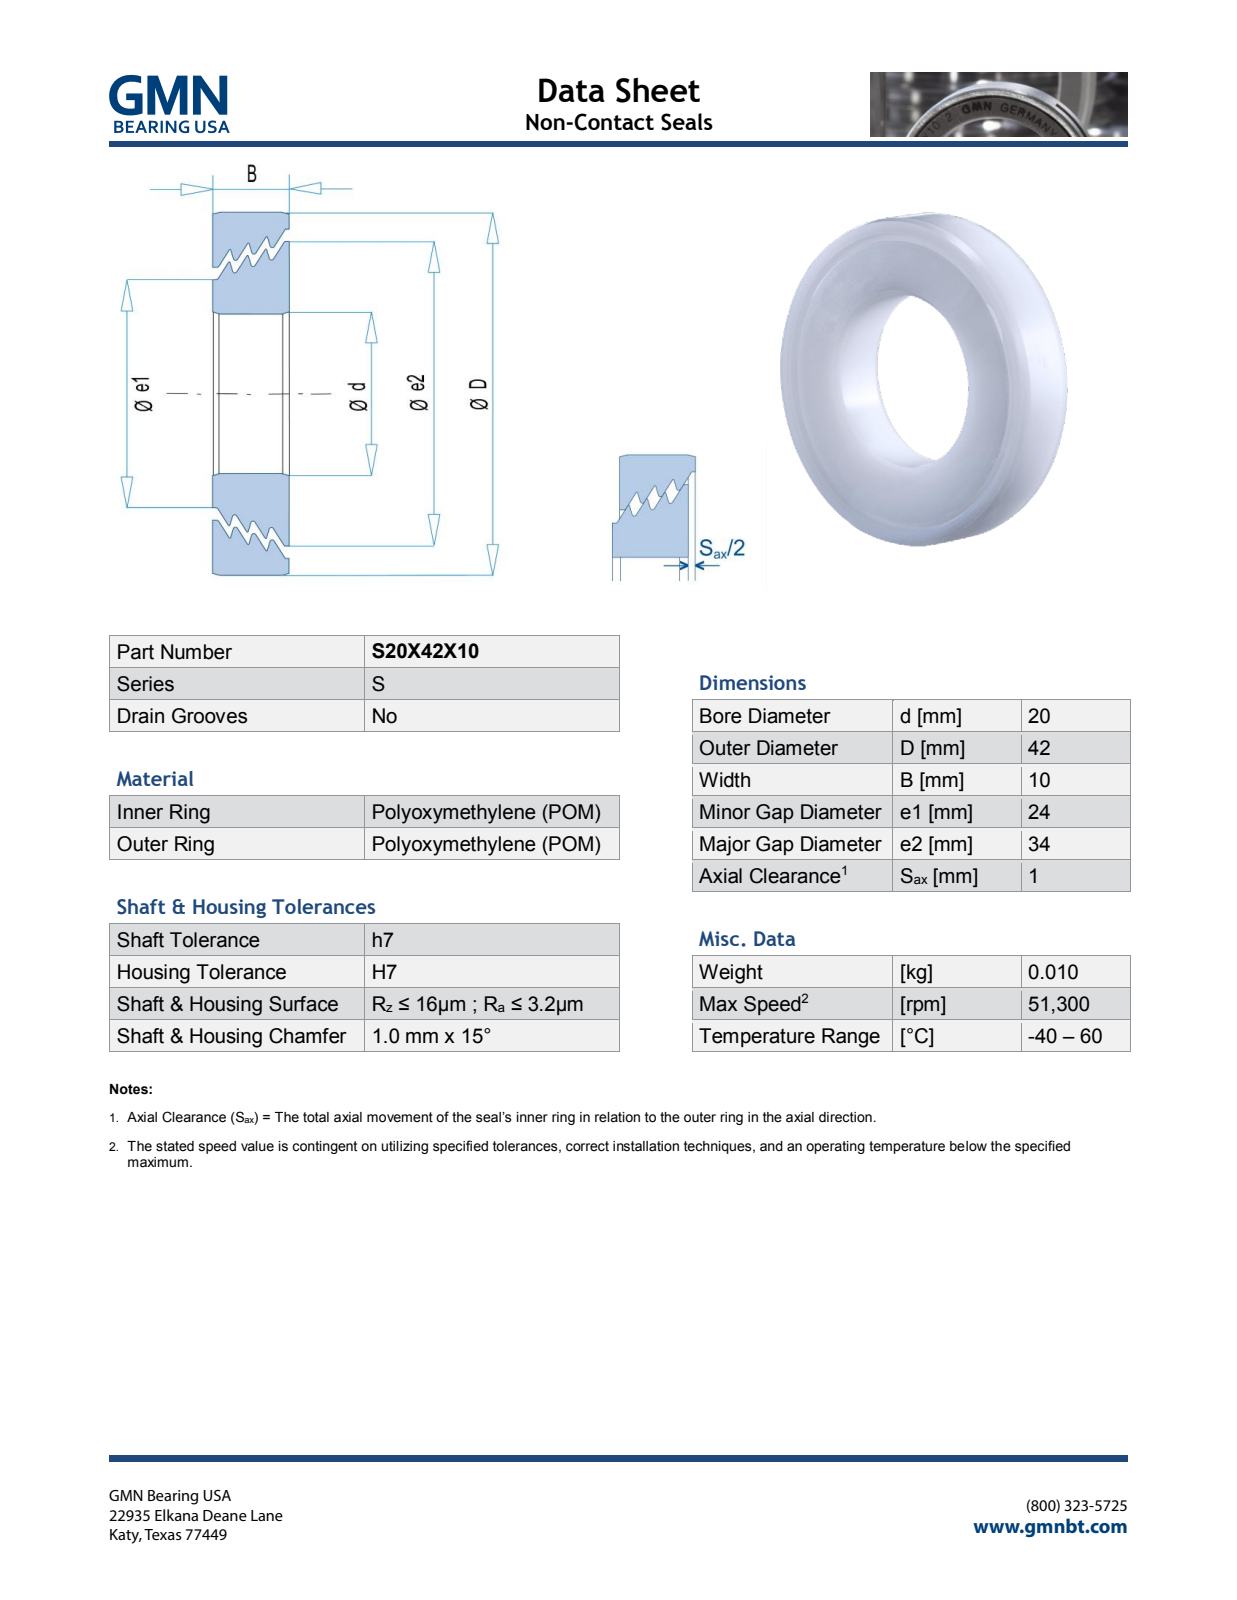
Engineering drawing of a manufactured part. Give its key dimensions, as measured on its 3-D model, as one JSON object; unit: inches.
{"part_name": "S20X42X10_PRT", "step_written_by": "PRO/ENGINEER BY PARAMETRIC TECHNOLOGY CORPORATION, 2013150 (AUTOMOTIVE_DESIGN)", "units": "inches", "bodies": {"solids": 2, "faces": 613, "planar": 533, "cylindrical": 12, "other": 68}, "overall_size": [1.654, 1.654, 0.396], "volume_in3": 0.604, "surface_area_in2": 11.97, "round_holes": [[0.787, 1], [1.009, 1], [1.403, 1]], "round_bosses_or_shafts": [[1.654, 1], [1.339, 1], [0.945, 1]], "face_to_face_distances": [0.394, 0.396, 0.072, 0.063, 0.051, 0.054, 0.031, 0.072, 0.032, 0.06]}
